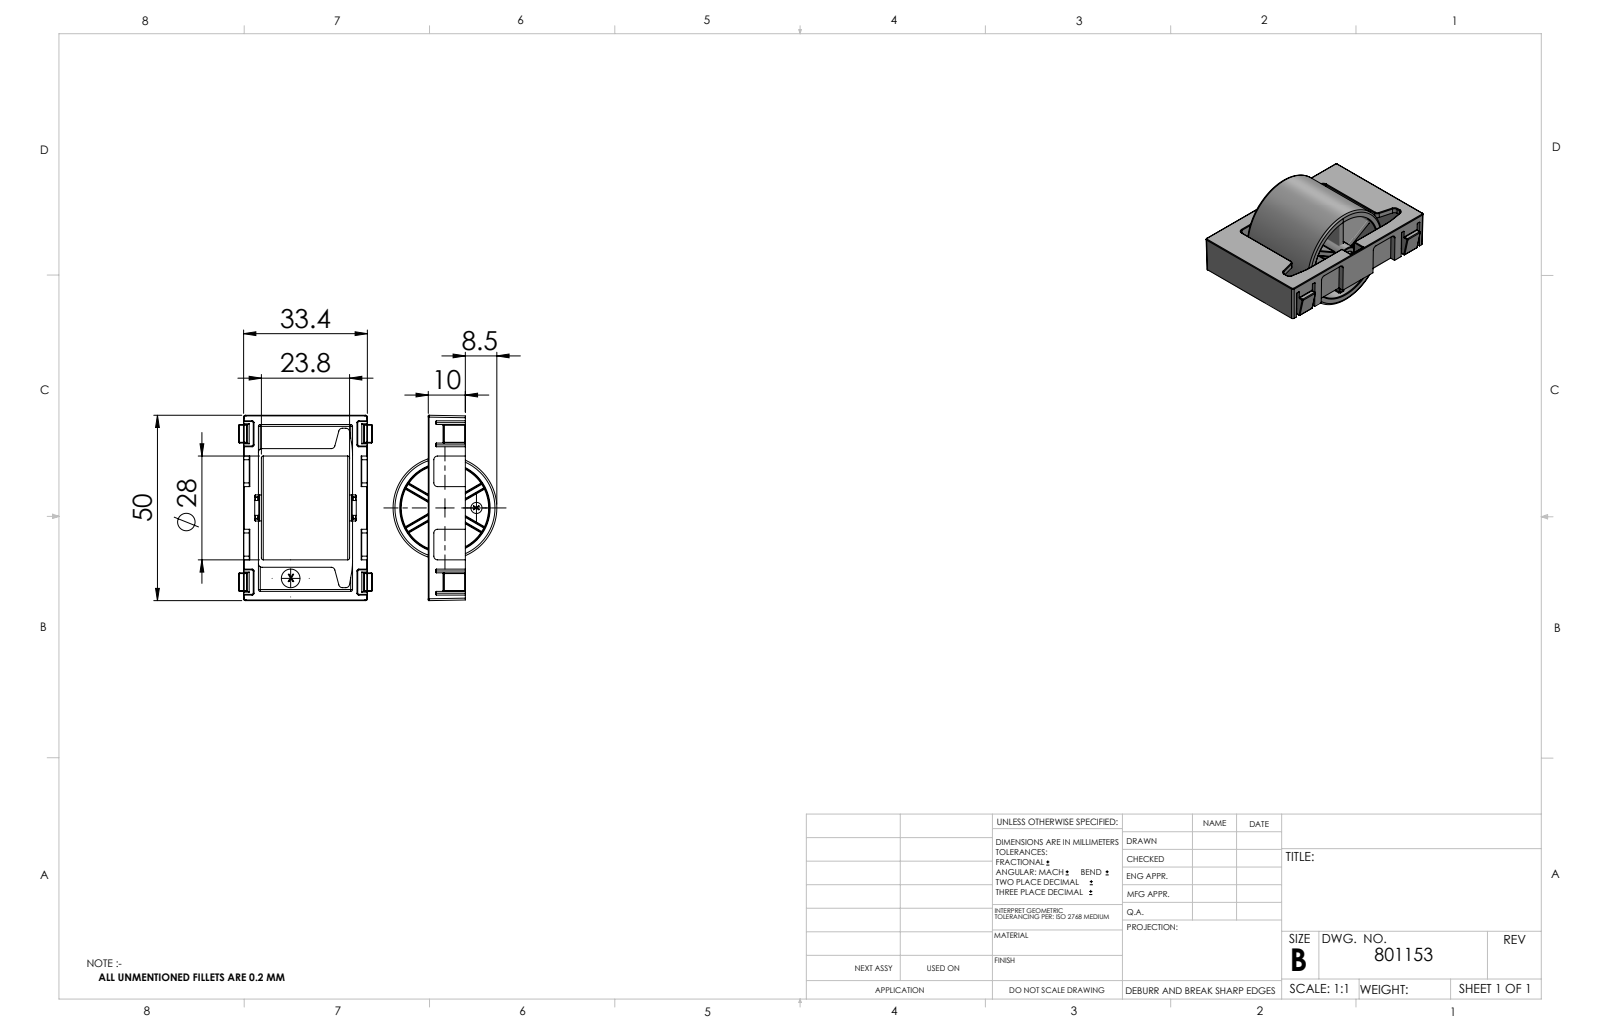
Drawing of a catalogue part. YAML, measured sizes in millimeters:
part_name: "801153_c_1"
step_written_by: "SolidWorks 2014 (CONFIG_CONTROL_DESIGN)"
units: millimeters
bodies: {solids: 3, faces: 744, planar: 172, cylindrical: 290, other: 282}
overall_size: [49.99, 35.9, 28]
volume: 11293
surface_area: 13212
round_holes:
  - {diameter: 4.2, count: 1}
  - {diameter: 24, count: 1}
round_bosses_or_shafts:
  - {diameter: 28, count: 1}
  - {diameter: 7, count: 1}
  - {diameter: 5.03, count: 1}
  - {diameter: 4, count: 1}
  - {diameter: 3, count: 1}
partial_cylinders:
  - {radius: 0.2, count: 144}
  - {radius: 0.5, count: 22}
  - {radius: 1, count: 12}
  - {radius: 0.1, count: 2}
  - {radius: 20, count: 2}
  - {radius: 2.05, count: 1}
face_to_face_distances: [1.5, 12.3, 13.1, 0.8, 10, 21.75, 23.25, 25.4, 2, 8.5]
